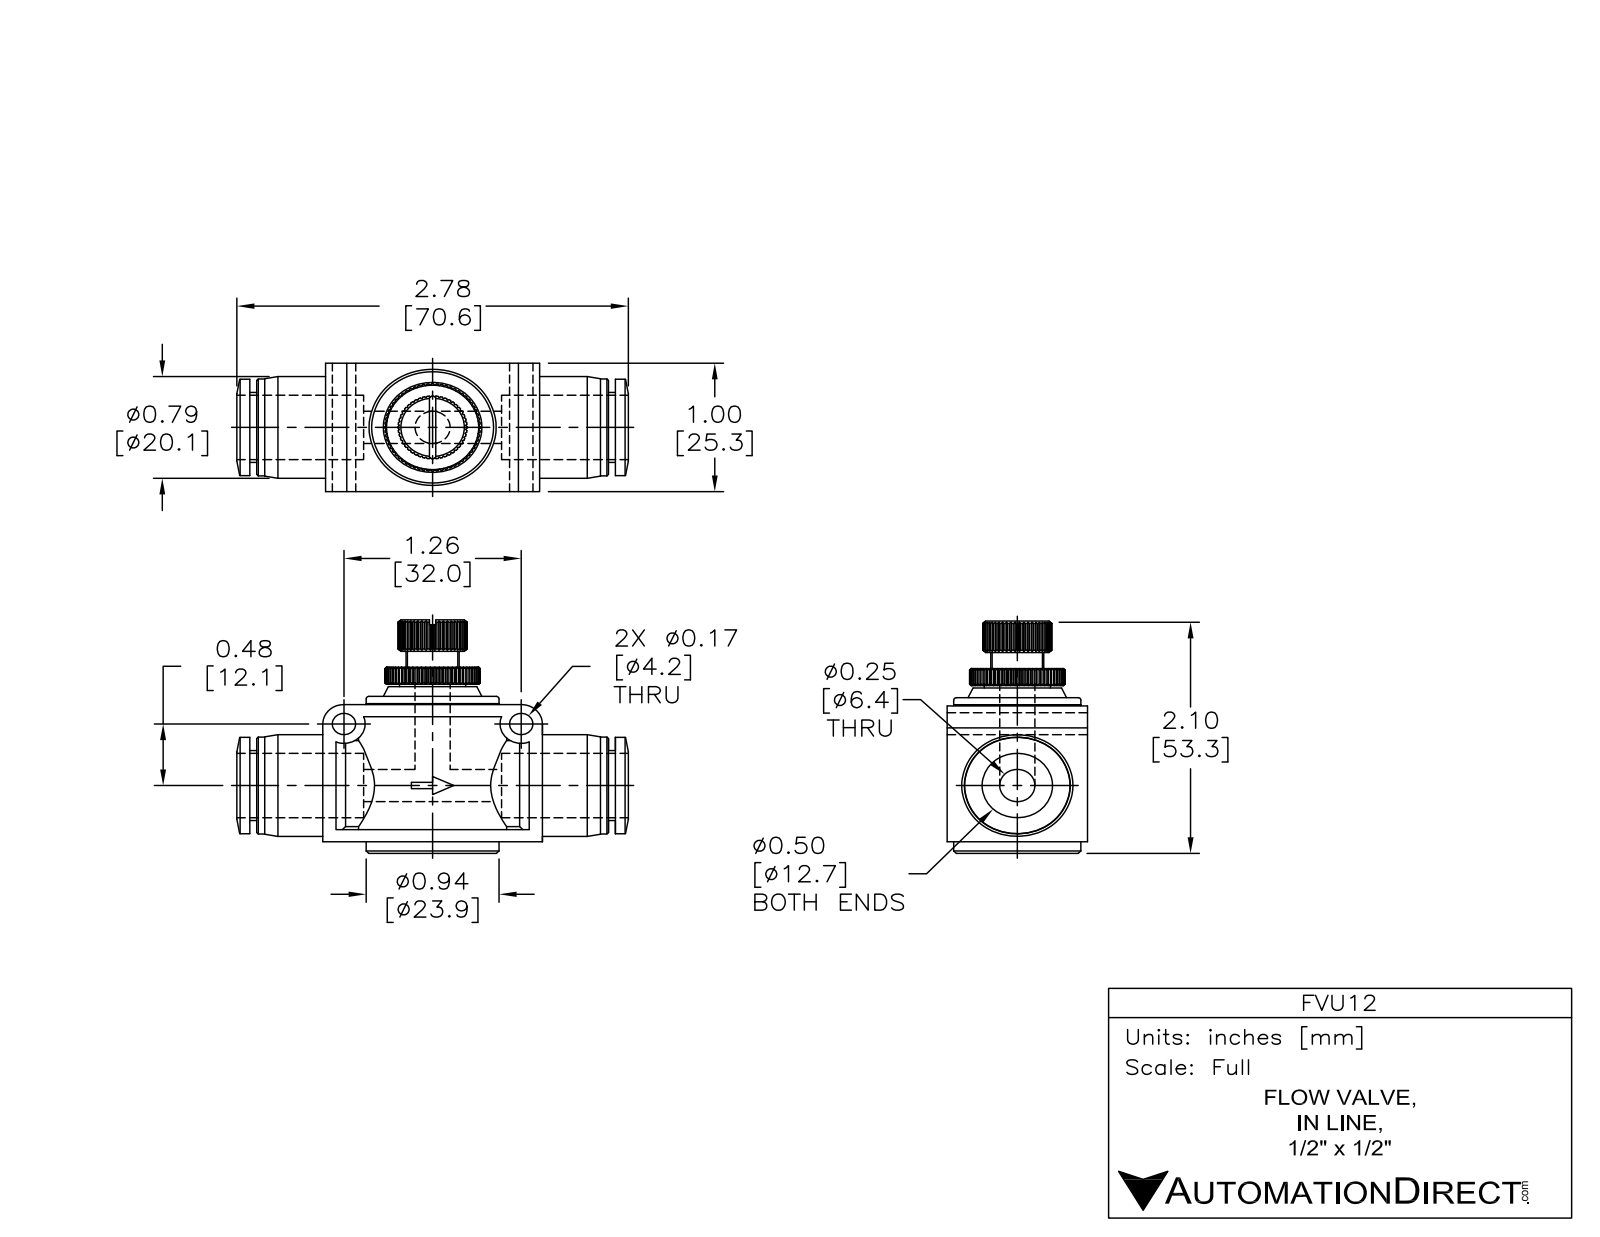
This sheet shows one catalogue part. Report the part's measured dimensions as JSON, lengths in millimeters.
{"part_name": "FVU12", "step_written_by": "SolidWorks 2015 (AUTOMOTIVE_DESIGN)", "units": "millimeters", "bodies": {"solids": 1, "faces": 623, "planar": 287, "cylindrical": 168, "other": 168}, "overall_size": [73.9, 53.5, 26.5], "volume_mm3": 31320, "surface_area_mm2": 14560, "round_holes": [[4.4, 2], [10, 1], [13, 1]], "round_bosses_or_shafts": [[24, 1], [24, 1], [21, 1], [20, 1], [19.9, 1], [17.4, 1], [14.5, 1], [12.5, 1]], "partial_cylinders_radius": [[4, 2], [6.5, 1], [9, 1], [13.6, 1]], "face_to_face_distances": [2.5, 25, 2.4, 29.9, 27.5, 26.5, 4.9, 26.3, 14.3, 54.7], "hole_center_spacings": [32.4]}
